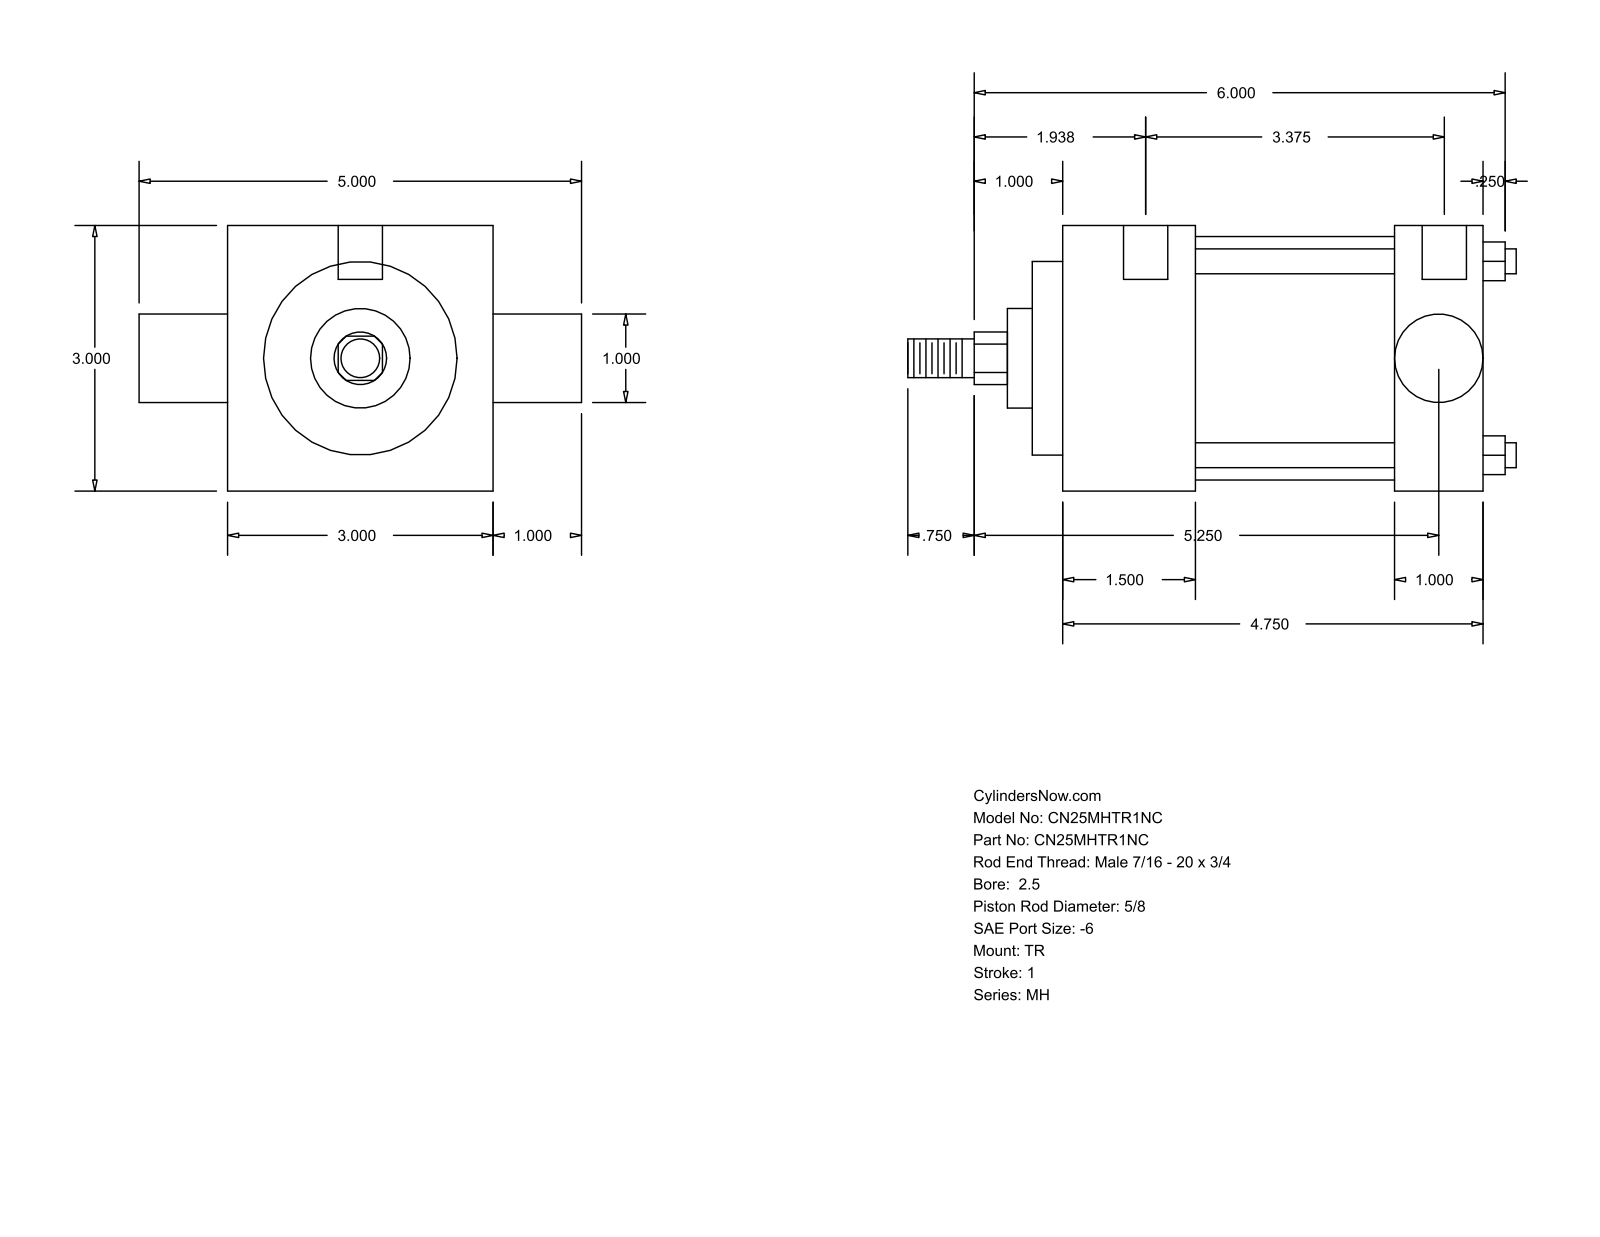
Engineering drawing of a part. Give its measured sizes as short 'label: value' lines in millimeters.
name: MH_TR__0250_0.625
written by: GSSL Pune (CONFIG_CONTROL_DESIGN)
unit: mm
bodies: 0 solids, 86 faces (61 planar, 25 cylindrical, 0 other)
size: 174.62 × 127 × 76.2
holes: 3× ⌀5.56, 2× ⌀12.7
bosses: 4× ⌀7.14, 1× ⌀69.85, 1× ⌀55.55, 1× ⌀28.57, 1× ⌀25.35, 1× ⌀15.88, 1× ⌀11.11
rounds: 1× R7.54
face distances: 76.2, 120.65, 25.4, 57.15, 82.55, 38.1, 95.25, 8.73, 46.83, 103.98
hole spacings: 3.17, 4.76, 85.73, 88.9, 90.49, 93.66
